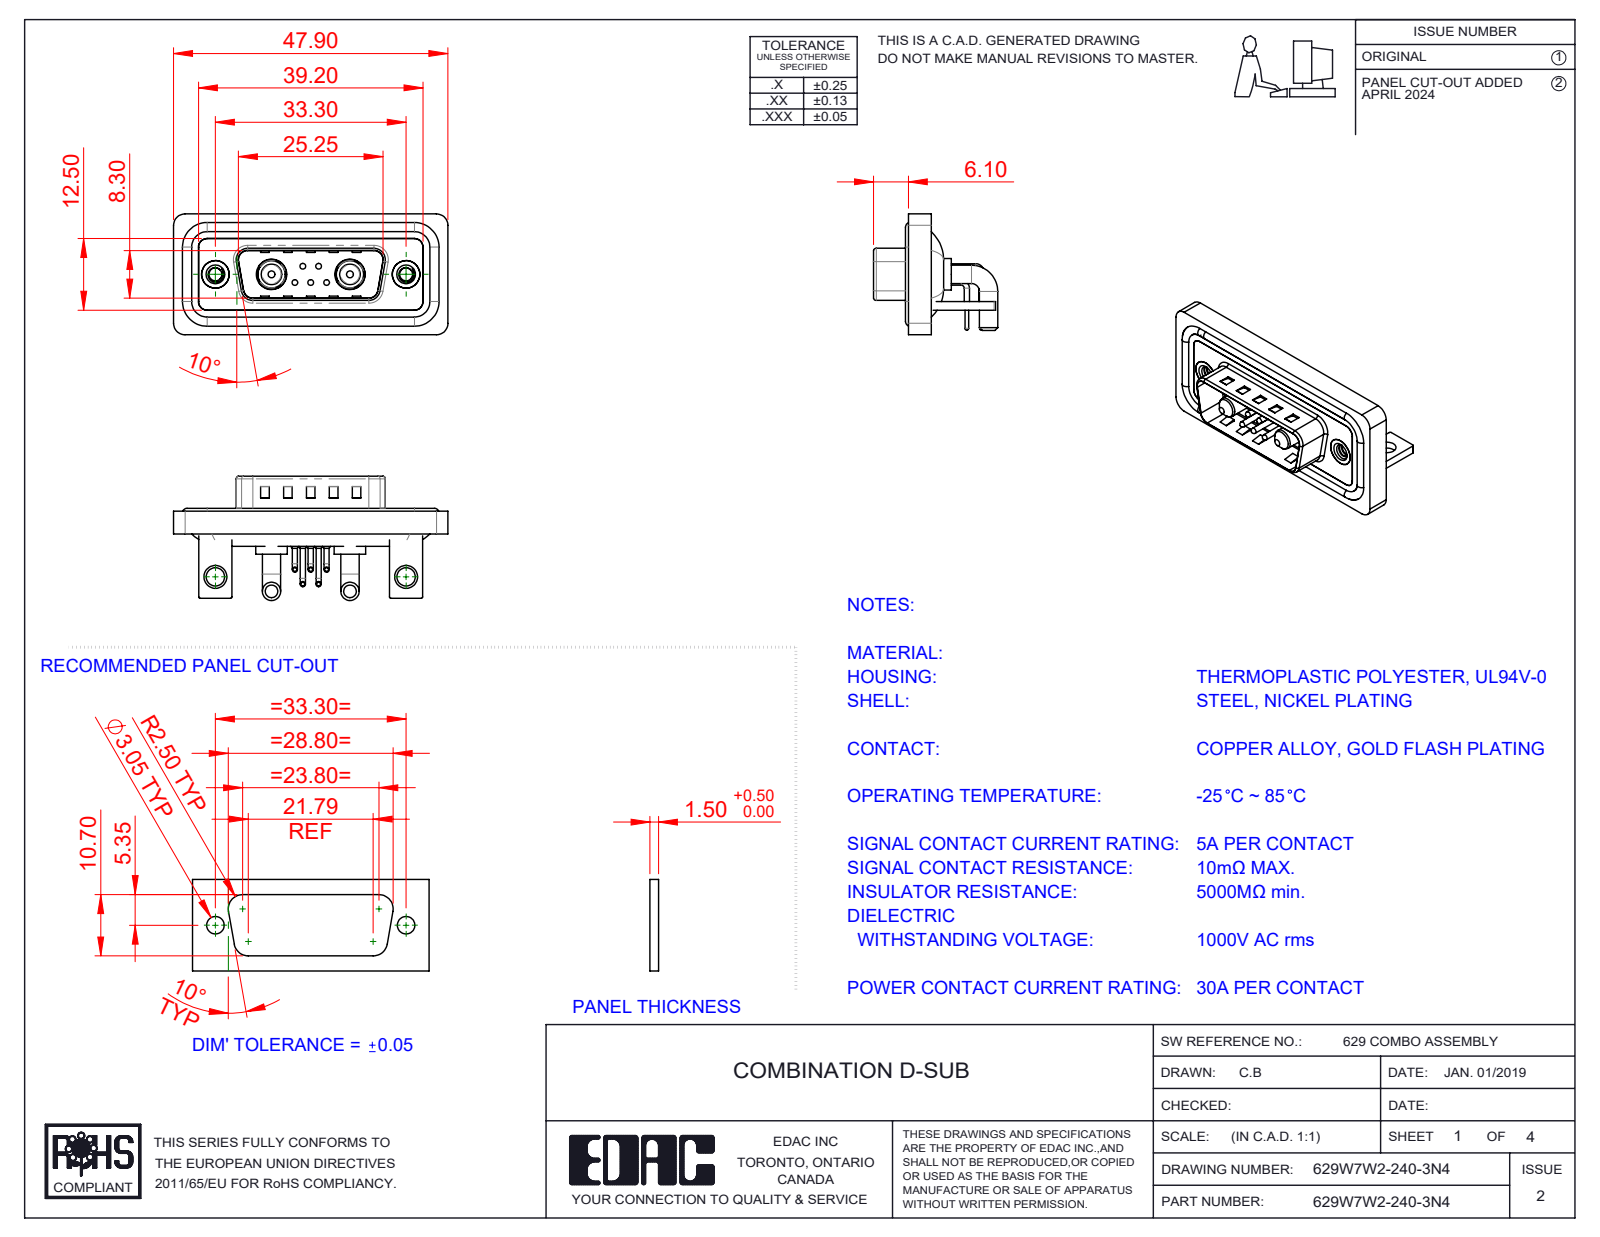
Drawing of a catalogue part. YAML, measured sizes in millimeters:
part_name: "629Combo Housing_7W2; 629Combo Stabilizer Bracket; 629Combo Threaded Rivet_3; 629Combo Shell Rear_15 Contacts (+6 more)"
step_written_by: "SolidWorks 2023 (CONFIG_CONTROL_DESIGN)"
units: millimeters
bodies: {solids: 18, faces: 1123, planar: 537, cylindrical: 424, other: 162}
overall_size: [47.9, 21.7, 21.1]
volume: 6014
surface_area: 9764
round_holes:
  - {diameter: 0.75, count: 5}
  - {diameter: 1.6, count: 5}
  - {diameter: 2, count: 5}
  - {diameter: 2.26, count: 2}
  - {diameter: 3.2, count: 2}
  - {diameter: 4, count: 2}
  - {diameter: 4.8, count: 2}
  - {diameter: 4.85, count: 2}
  - {diameter: 5, count: 2}
  - {diameter: 5.3, count: 2}
round_bosses_or_shafts:
  - {diameter: 0.9, count: 10}
  - {diameter: 1.5, count: 5}
  - {diameter: 1, count: 5}
  - {diameter: 0.65, count: 5}
  - {diameter: 3.2, count: 4}
  - {diameter: 1.6, count: 4}
  - {diameter: 5.5, count: 2}
  - {diameter: 5.2, count: 2}
partial_cylinders:
  - {radius: 2, count: 21}
  - {radius: 1.5, count: 18}
  - {radius: 0.25, count: 16}
  - {radius: 0.5, count: 9}
  - {radius: 1.6, count: 8}
  - {radius: 1.01, count: 5}
  - {radius: 0.6, count: 4}
  - {radius: 0.65, count: 4}
face_to_face_distances: [0.4, 1.5, 0.8, 2.9, 2.1, 1.1, 1.6, 1.2, 3.7, 4.5]
hole_center_spacings: [3.16, 2.77, 9.8, 23.5, 33.3, 4.31, 4.33, 5.03]
